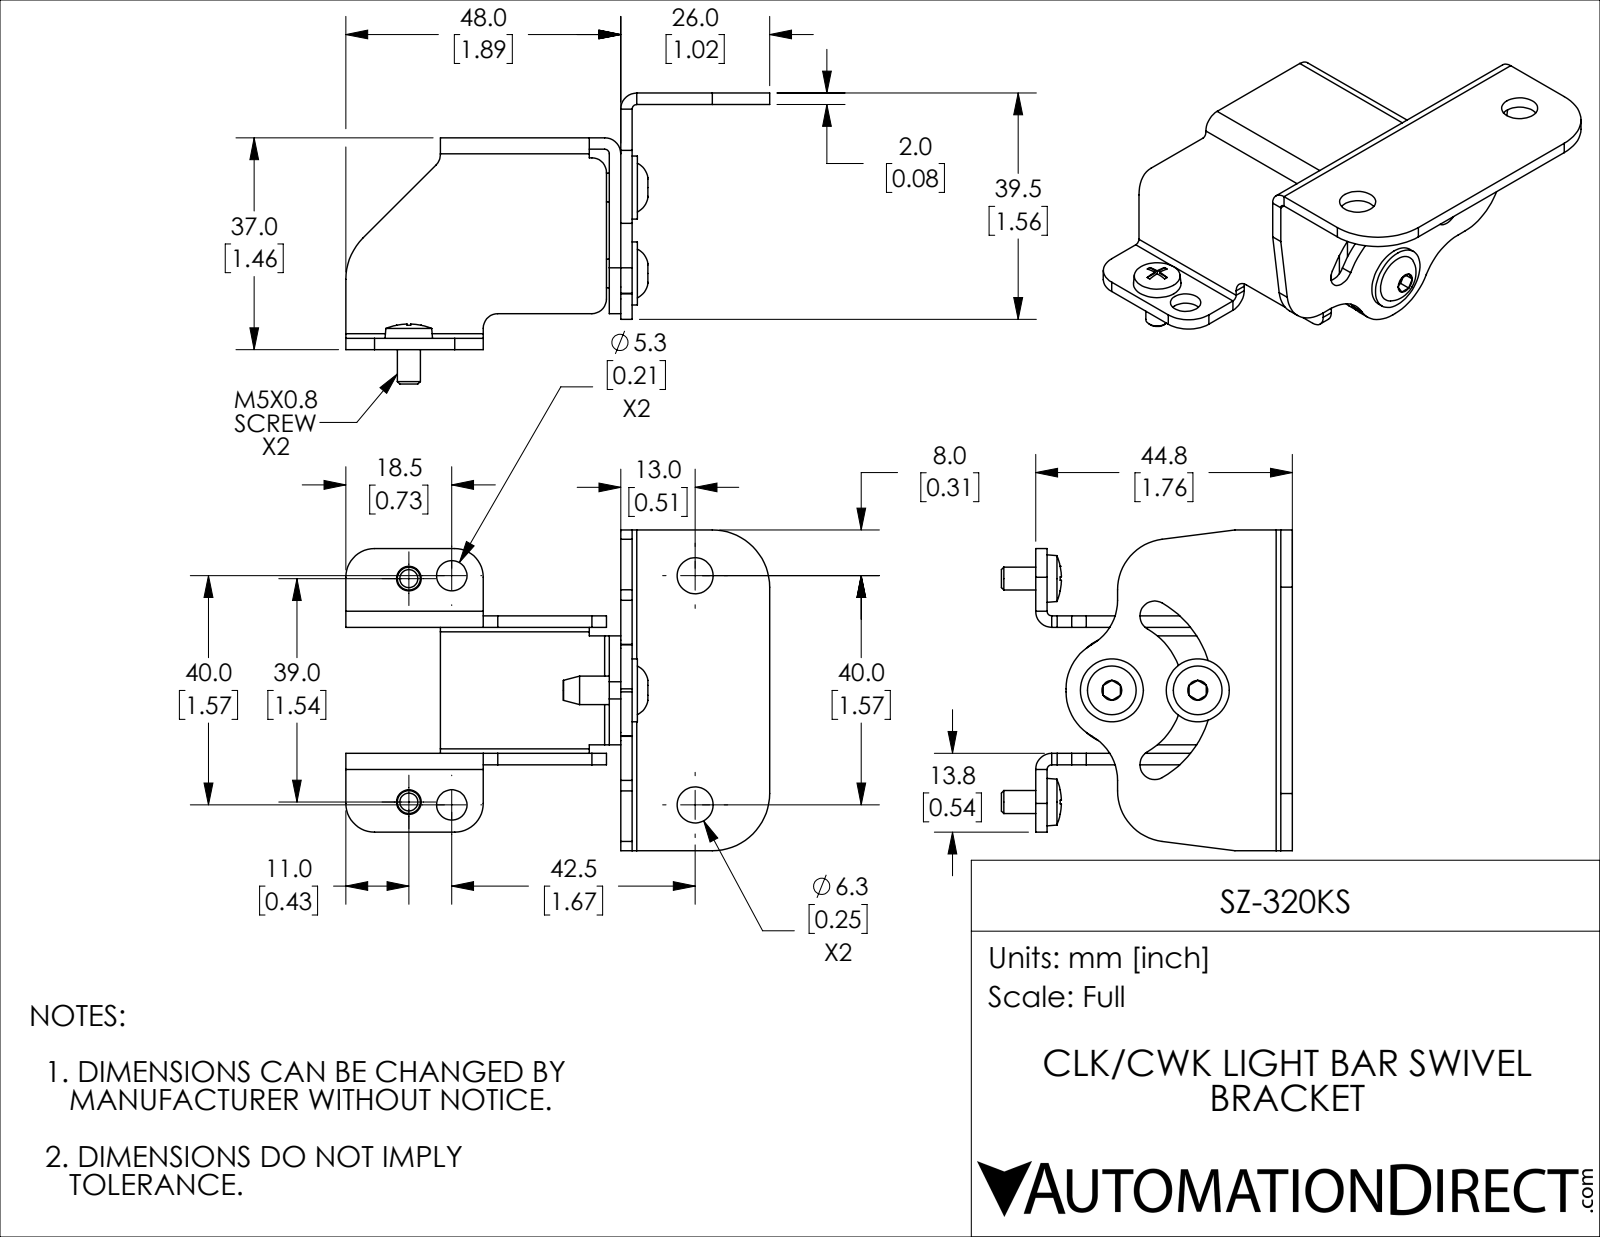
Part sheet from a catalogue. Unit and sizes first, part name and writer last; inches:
Units: inches
Overall size (bounding box): 2.913 × 2.205 × 2
Round holes (diameter × count): ⌀0.169 ×2, ⌀0.197 ×2, ⌀0.209 ×2, ⌀0.248 ×2, ⌀0.205 ×1
Round bosses / shafts (diameter × count): ⌀0.433 ×2, ⌀0.157 ×2
Partial cylindrical surfaces — rounded edges, fillets, slot ends (radius × count): R0.031 ×6, R0.11 ×6, R0.35 ×6, R0.1 ×4, R0.197 ×4, R0.102 ×2, R0.315 ×2, R0.394 ×2
Main face-to-face distances: 0.079, 0.945, 1.024, 0.866, 0.307, 1.685, 1.378, 0.386, 0.228, 1.299
Hole centre spacings: 0.296, 1.575, 1.583, 1.673, 1.969, 2.298, 2.509, 0.591
Volume: 0.919 in³ · Surface area: 26.23 in²
Bodies: 6 solids, 212 faces (118 planar, 72 cylindrical, 22 other)
Part name (STEP PRODUCT): SZ-320KS
STEP written by: SolidWorks 2018 (AUTOMOTIVE_DESIGN)
